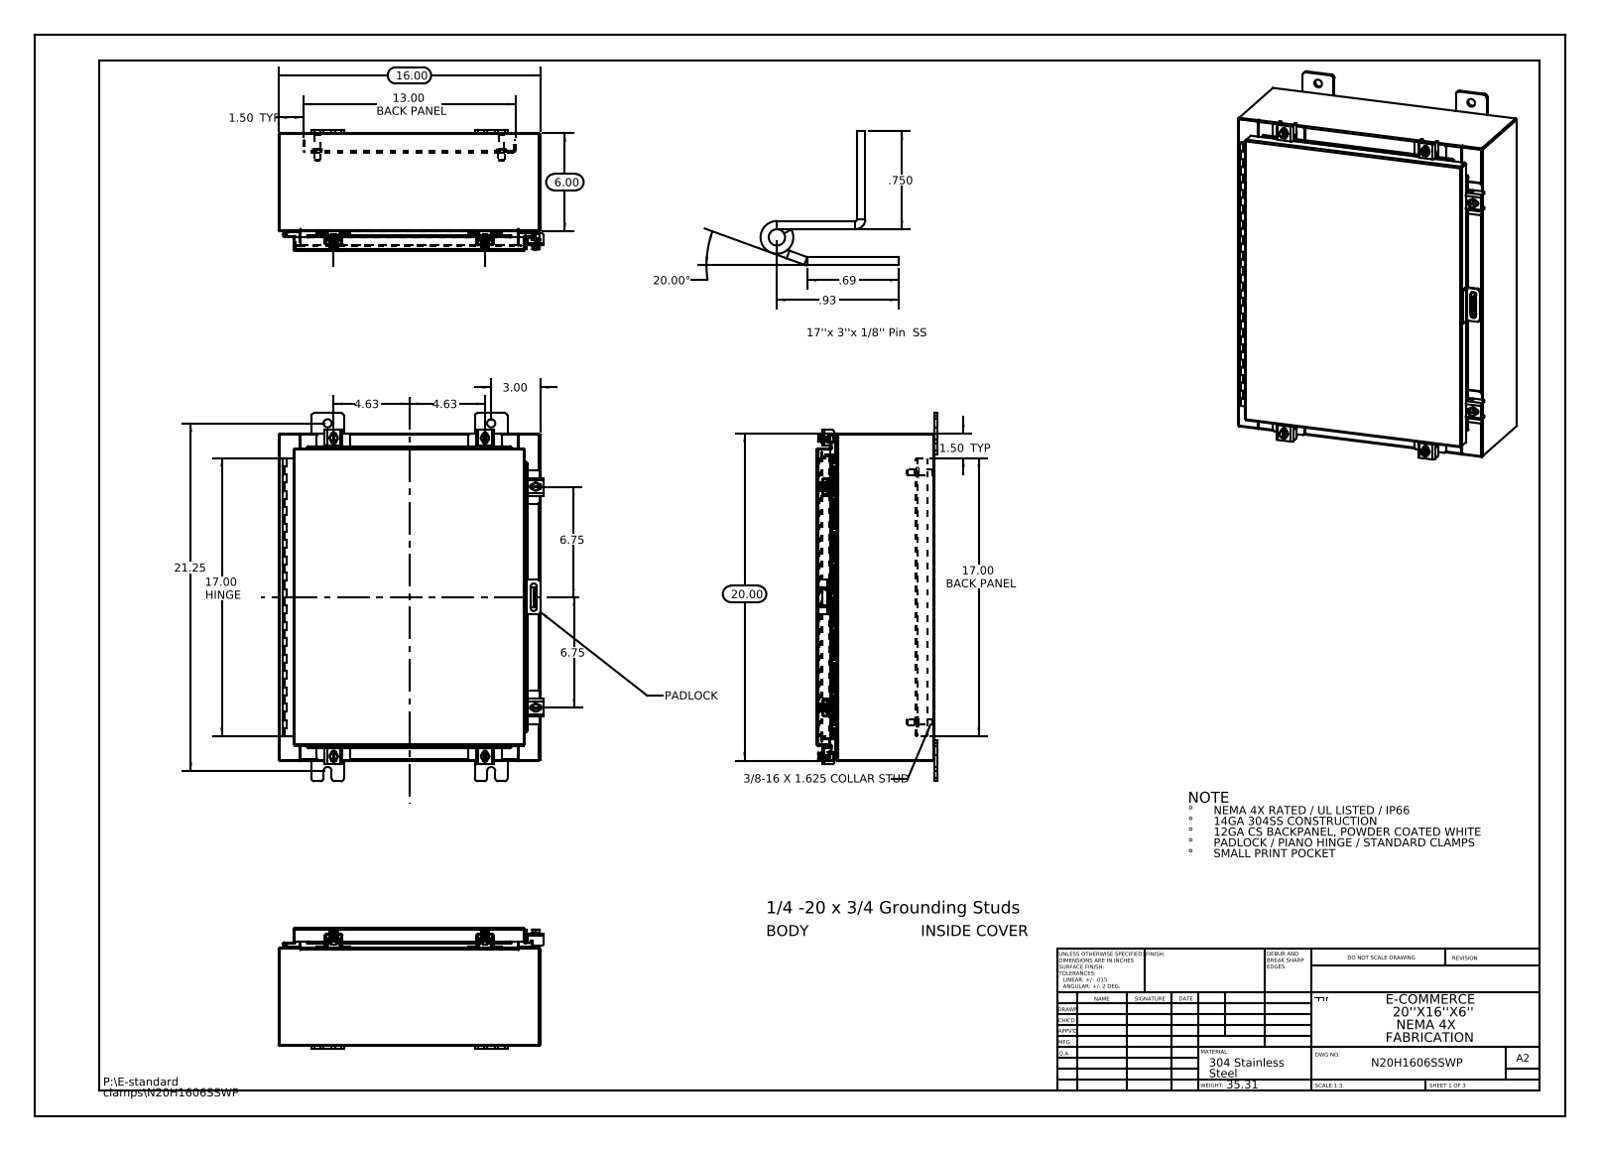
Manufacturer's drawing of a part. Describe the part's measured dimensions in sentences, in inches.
The part is named "N20H1606SSWP Backpanel; N20H1606SSWP Clamp Assembly; N20H1606SSWP Top; N20H1606SSWP 125 Pin Hinge (+8 more)". Its 3-D file was written by "SolidWorks 2013 (CONFIG_CONTROL_DESIGN)". It is 47 solids with 1613 faces: 860 planar, 657 cylindrical and 96 other. Overall it measures 22.5 by 16.211 by 7.389 inches. Its volume is 124.9 cubic inches and its surface area 3 149 square inches. Round holes: 8 of diameter 0.5, 6 of diameter 0.213, 6 of diameter 0.26, 2 of diameter 0.125, 1 of diameter 0.125. Round bosses or shafts: 7 of diameter 0.25, 6 of diameter 0.5, 6 of diameter 0.399, 4 of diameter 0.625, 4 of diameter 0.375, 4 of diameter 0.33. Partial cylindrical surfaces (rounded edges, fillets, slot ends): 30 of radius 0.06, 25 of radius 0.013, 24 of radius 0.19, 21 of radius 0.088, 12 of radius 0.12, 12 of radius 0.141, 10 of radius 0.125, 9 of radius 0.05. The main face-to-face distances are 0.075, 7.126, 7.201, 7.051, 0.104, 15.925, 1, 1.075, 6.051, 6.126. The hole center spacings are 17.38, 1.858, 2.276, 2.326, 2.326, 3.065, 4.297, 9.25.
